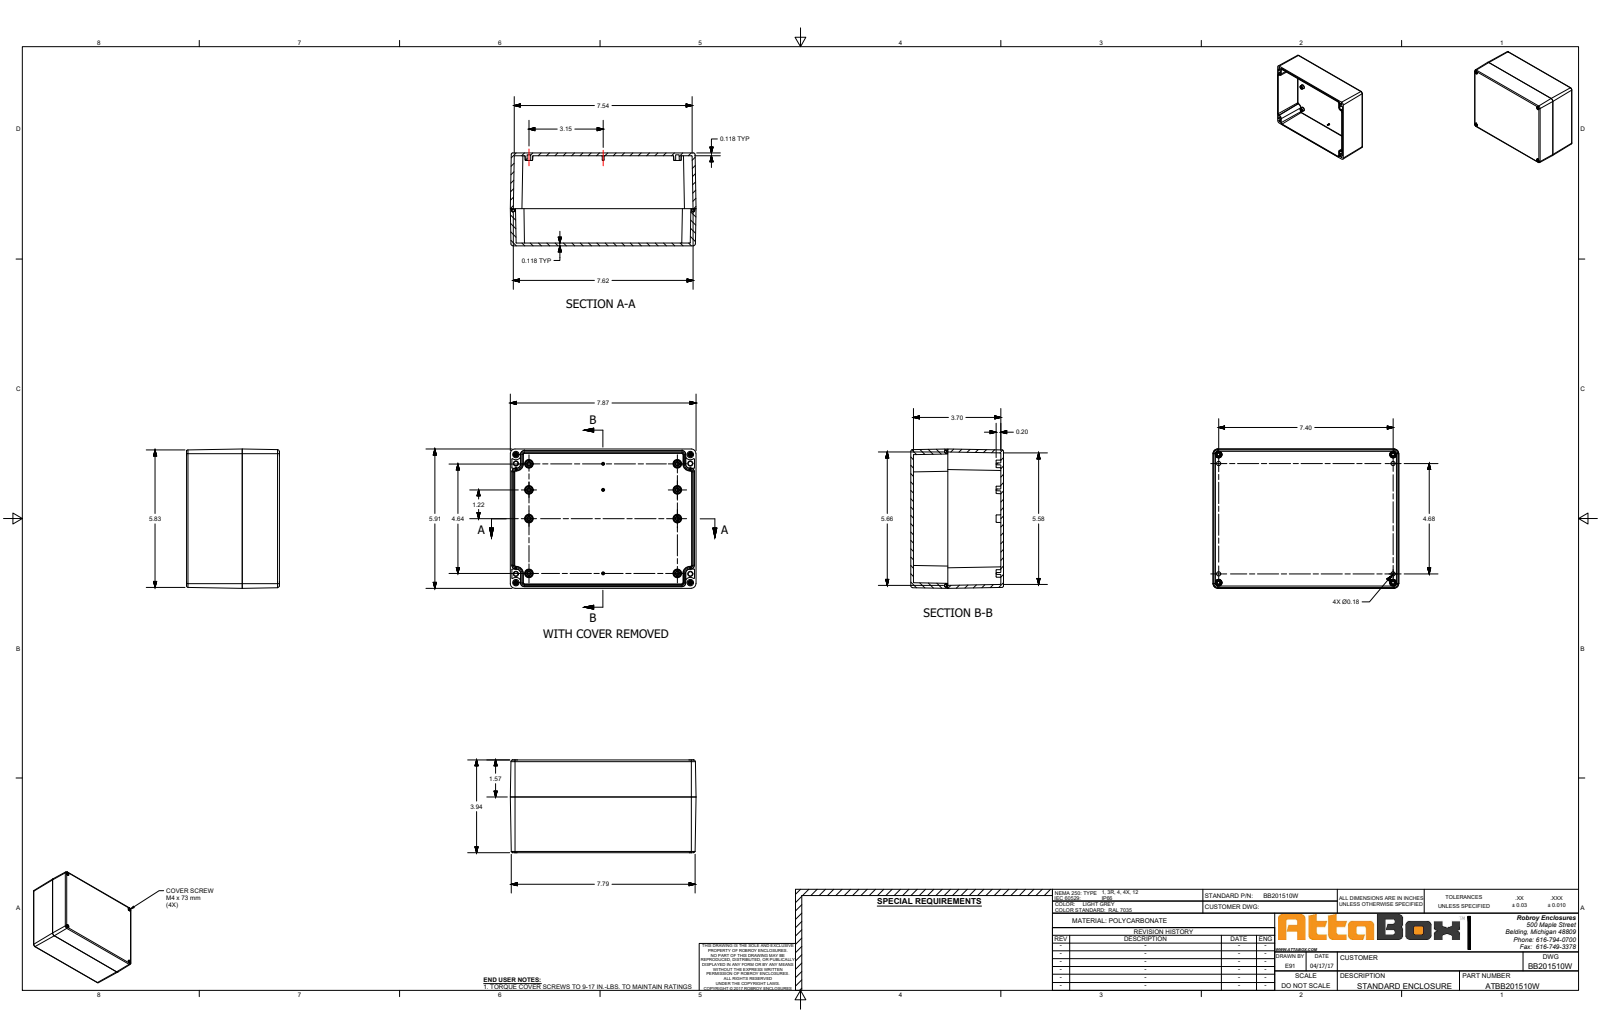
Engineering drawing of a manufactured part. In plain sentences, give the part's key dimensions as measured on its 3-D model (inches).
The part is named "BB201510W". Its 3-D file was written by "SolidWorks 2018 (AUTOMOTIVE_DESIGN)". It is 11 solids with 1723 faces: 622 planar, 448 cylindrical and 653 other. Overall it measures 7.874 by 5.906 by 3.937 inches. Its volume is 28.1 cubic inches and its surface area 443.9 square inches. Round holes: 4 of diameter 0.128, 4 of diameter 0.177, 4 of diameter 0.189, 4 of diameter 0.197, 4 of diameter 0.201, 4 of diameter 0.276, 4 of diameter 0.291. Round bosses or shafts: 4 of diameter 0.268, 4 of diameter 0.173, 4 of diameter 0.157, 4 of diameter 0.13. Partial cylindrical surfaces (rounded edges, fillets, slot ends): 32 of radius 0.02, 32 of radius 0.055, 16 of radius 0.039, 14 of radius 0.016, 12 of radius 0.079, 8 of radius 0.201, 4 of radius 0.059, 4 of radius 0.102. The main face-to-face distances are 0.118, 3.819, 0.126, 3.937, 3.701, 5.906, 5.78, 5.693, 5.567, 0.213. The hole center spacings are 0.378, 5.055, 7.402, 7.411, 8.963, 4.677, 5.433, 8.756.
